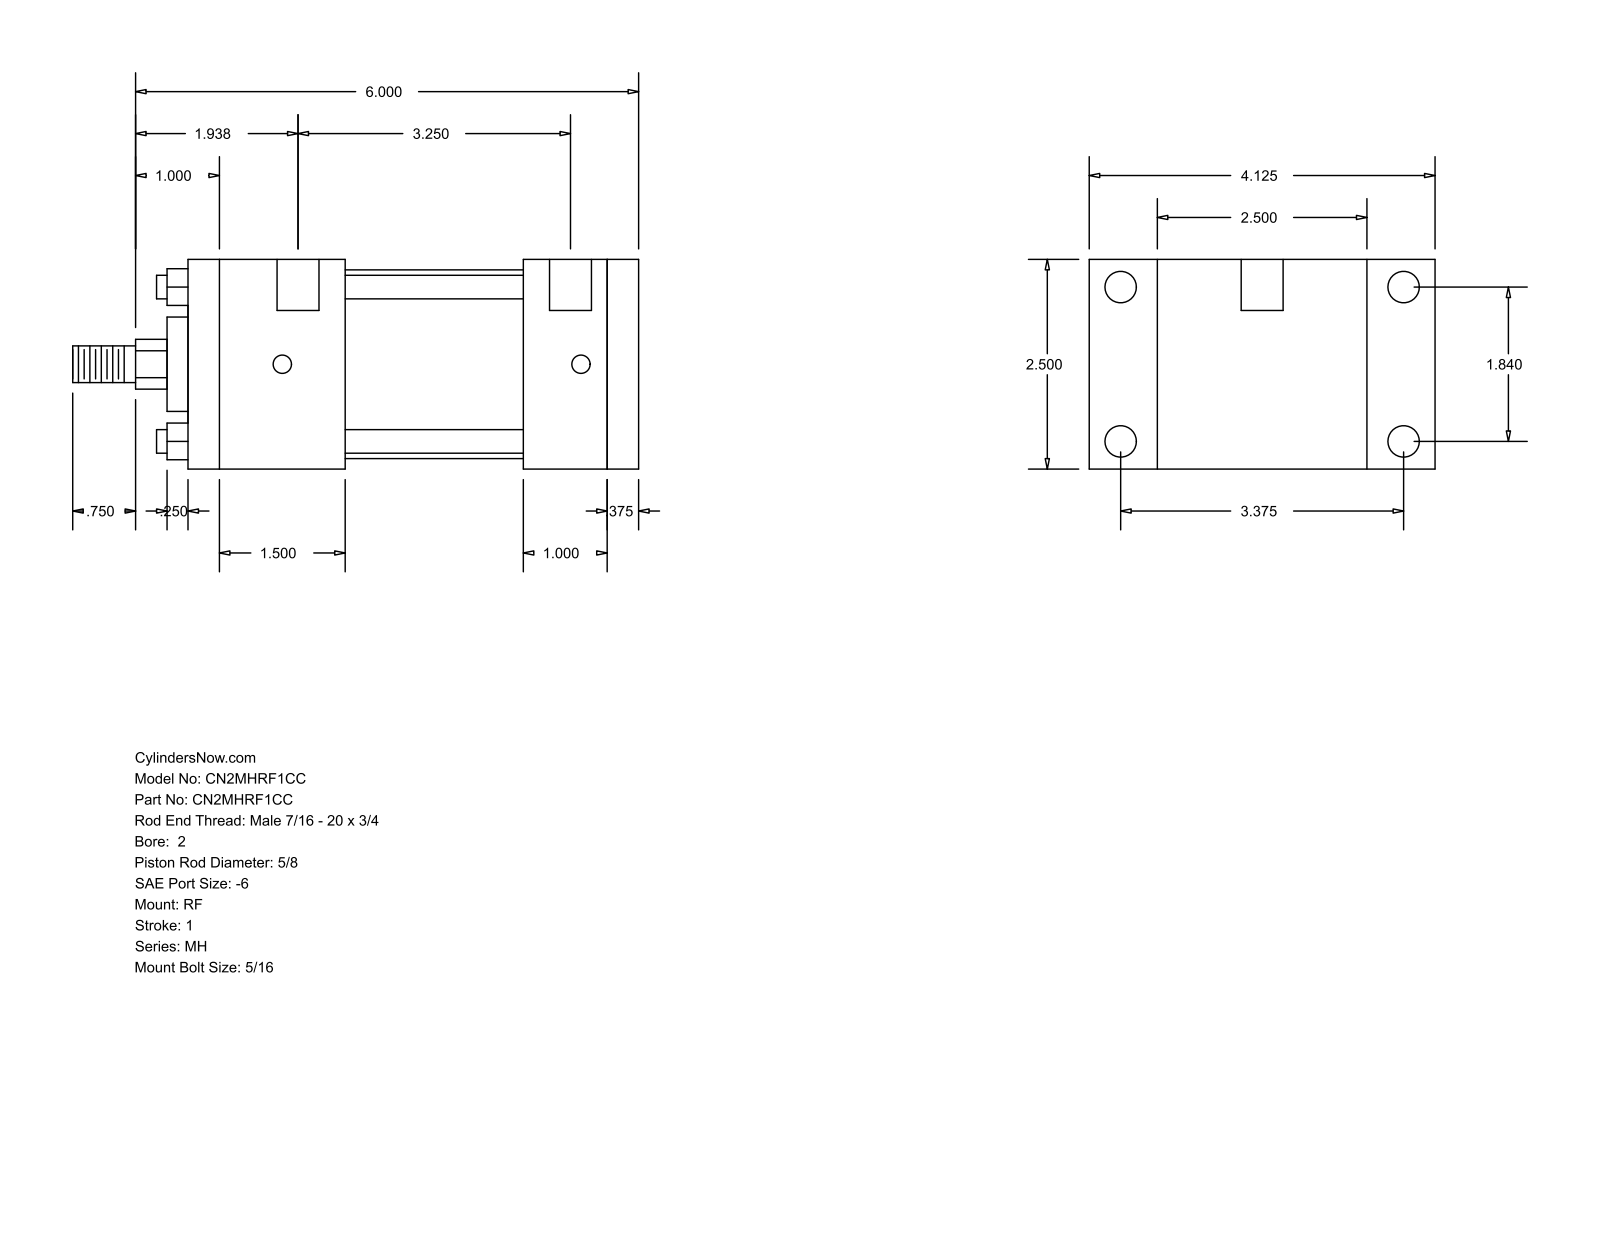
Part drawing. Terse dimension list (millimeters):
name: MH_RF__0200_0.625
written by: GSSL Pune (CONFIG_CONTROL_DESIGN)
unit: mm
bodies: 0 solids, 92 faces (64 planar, 28 cylindrical, 0 other)
size: 171.45 × 104.78 × 63.5
holes: 4× ⌀5.56, 4× ⌀9.53, 2× ⌀12.7
bosses: 4× ⌀7.14, 1× ⌀57.15, 1× ⌀28.57, 1× ⌀15.88, 1× ⌀11.11
rounds: 1× R7.54
face distances: 63.5, 136.52, 127, 9.52, 53.97, 34.93, 47.62, 101.59, 79.38, 88.9
hole spacings: 46.74, 85.72, 90.49, 97.63, 3.18, 4.76, 82.55, 85.73
